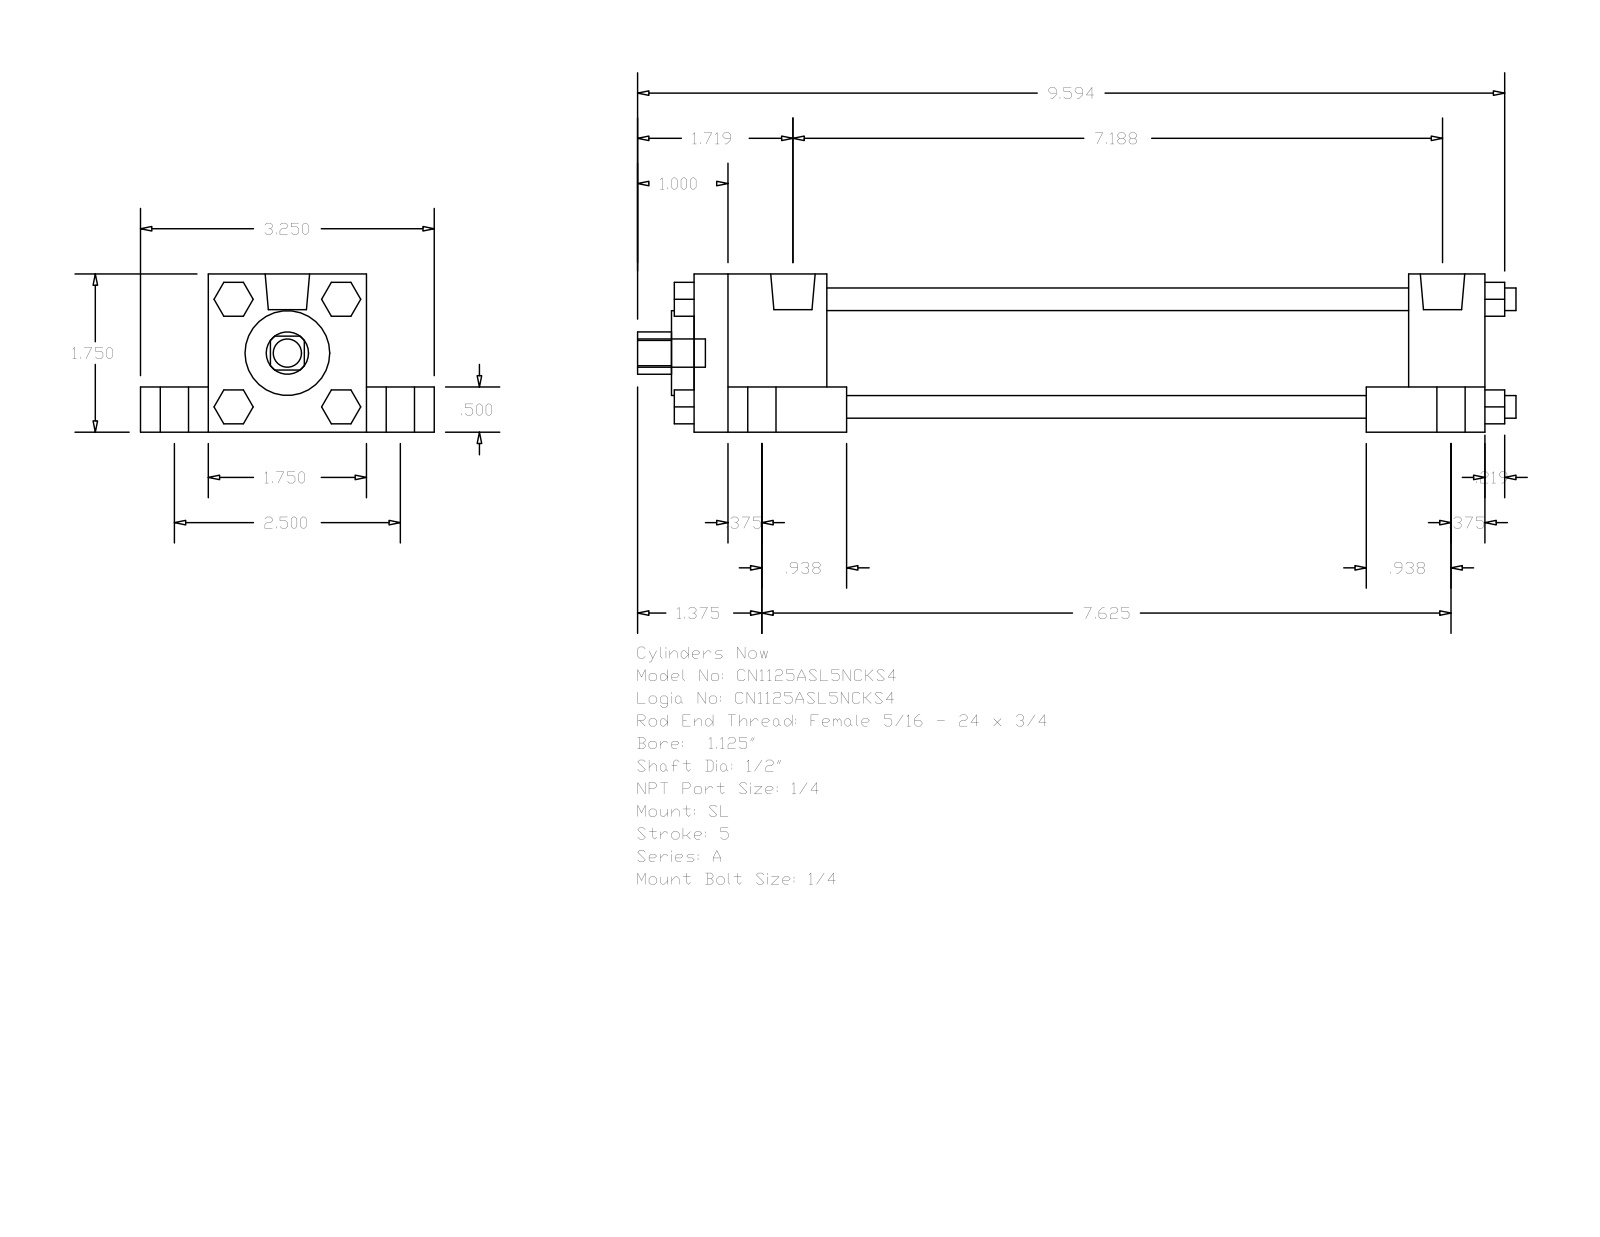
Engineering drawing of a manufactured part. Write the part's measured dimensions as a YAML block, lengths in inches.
part_name: "A_SL__0112_0.5"
step_written_by: "GSSL Pune (CONFIG_CONTROL_DESIGN)"
units: inches
bodies: {solids: 0, faces: 150, planar: 114, cylindrical: 36, other: 0}
overall_size: [9.719, 3.25, 1.75]
round_holes:
  - {diameter: 0.5, count: 1}
  - {diameter: 0.937, count: 1}
  - {diameter: 1.255, count: 1}
round_bosses_or_shafts:
  - {diameter: 0.313, count: 5}
  - {diameter: 0.563, count: 4}
  - {diameter: 0.25, count: 4}
  - {diameter: 0.219, count: 4}
  - {diameter: 0.492, count: 2}
partial_cylinders:
  - {radius: 0.234, count: 1}
face_to_face_distances: [1.75, 1.25, 0.5, 0.75, 2.5, 7.281, 8.75, 7.906, 0.844, 1.469]
